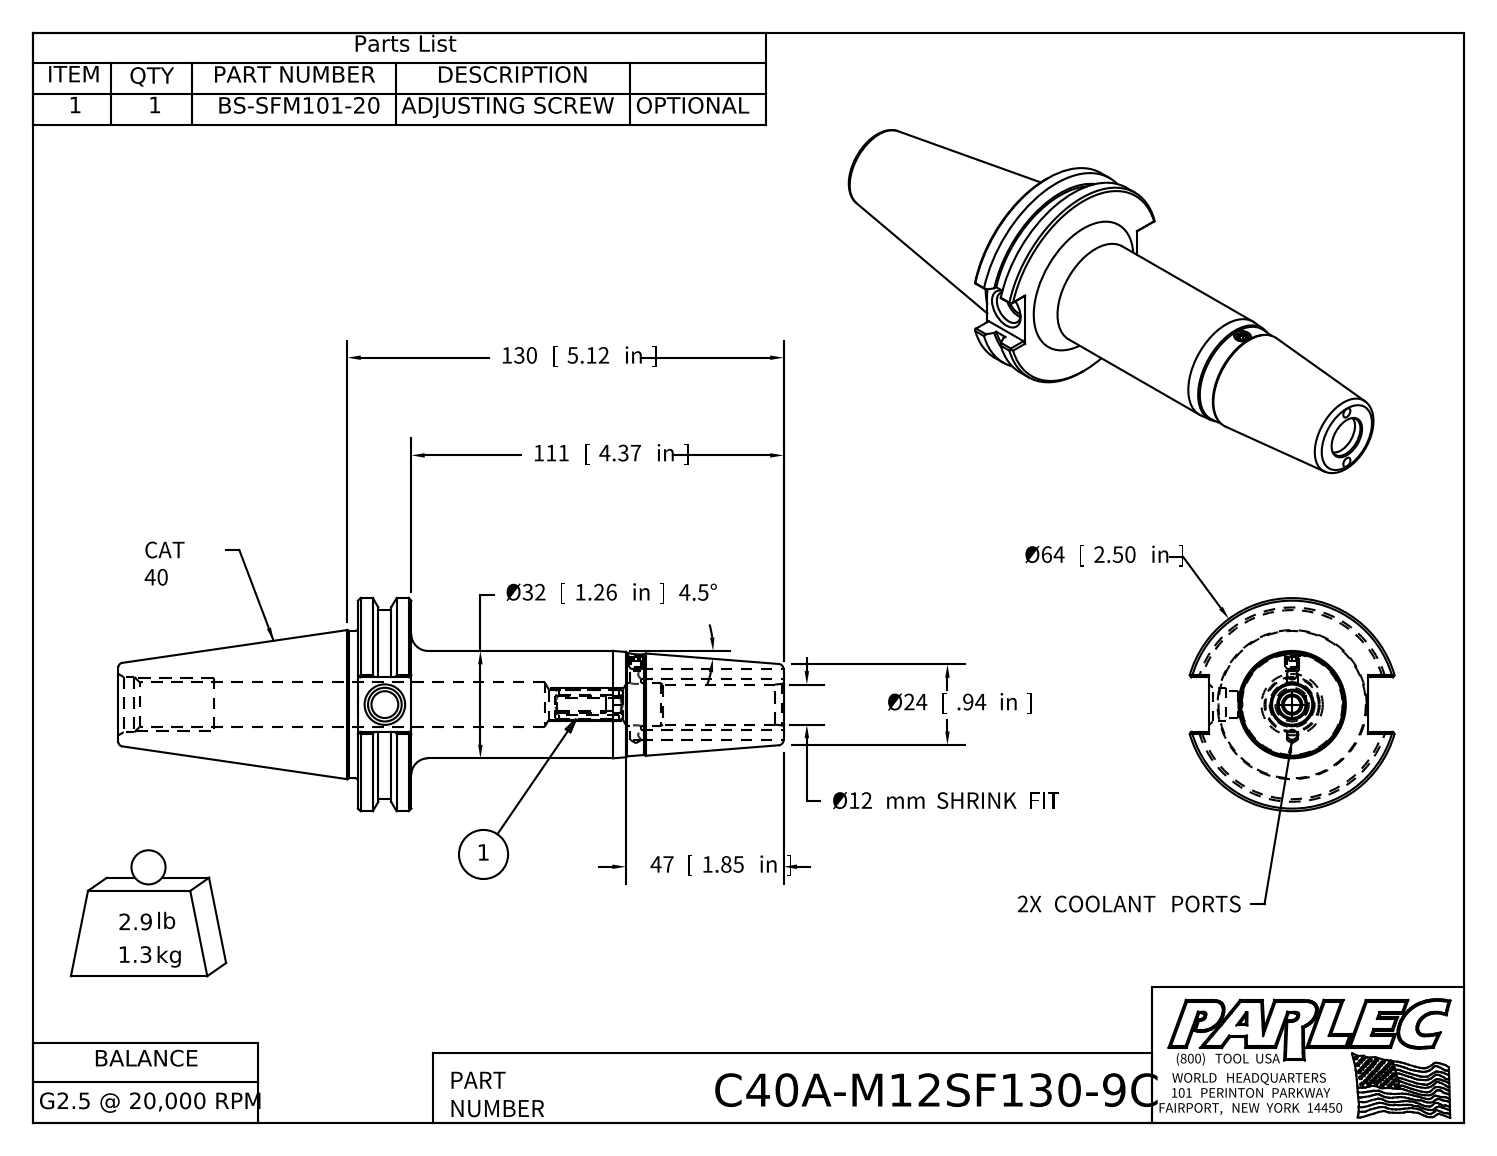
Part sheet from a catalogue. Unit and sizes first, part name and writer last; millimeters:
Units: millimetres
Overall size (bounding box): 198.26 × 63.5 × 61.05
Round holes (diameter × count): ⌀3 ×2, ⌀3.25 ×1, ⌀5 ×1, ⌀8 ×1, ⌀8.92 ×1, ⌀10.05 ×1, ⌀11.97 ×1, ⌀12.74 ×1, ⌀13.39 ×1, ⌀16.46 ×1
Round bosses / shafts (diameter × count): ⌀63.5 ×1, ⌀56.36 ×1, ⌀43.94 ×1, ⌀32 ×1
Main face-to-face distances: 15.88, 126.83, 110.95, 16.26, 47.25, 71.43, 87.31, 198.26, 81.31, 9.88
Hole centre spacings: 9, 18
Volume: 167 267 mm³ · Surface area: 35 297 mm²
Bodies: 1 solid, 82 faces (33 planar, 20 cylindrical, 29 other)
Part name (STEP PRODUCT): C40A-M12SF130-9C
STEP written by: Autodesk Inventor 2018 (AUTOMOTIVE_DESIGN)
